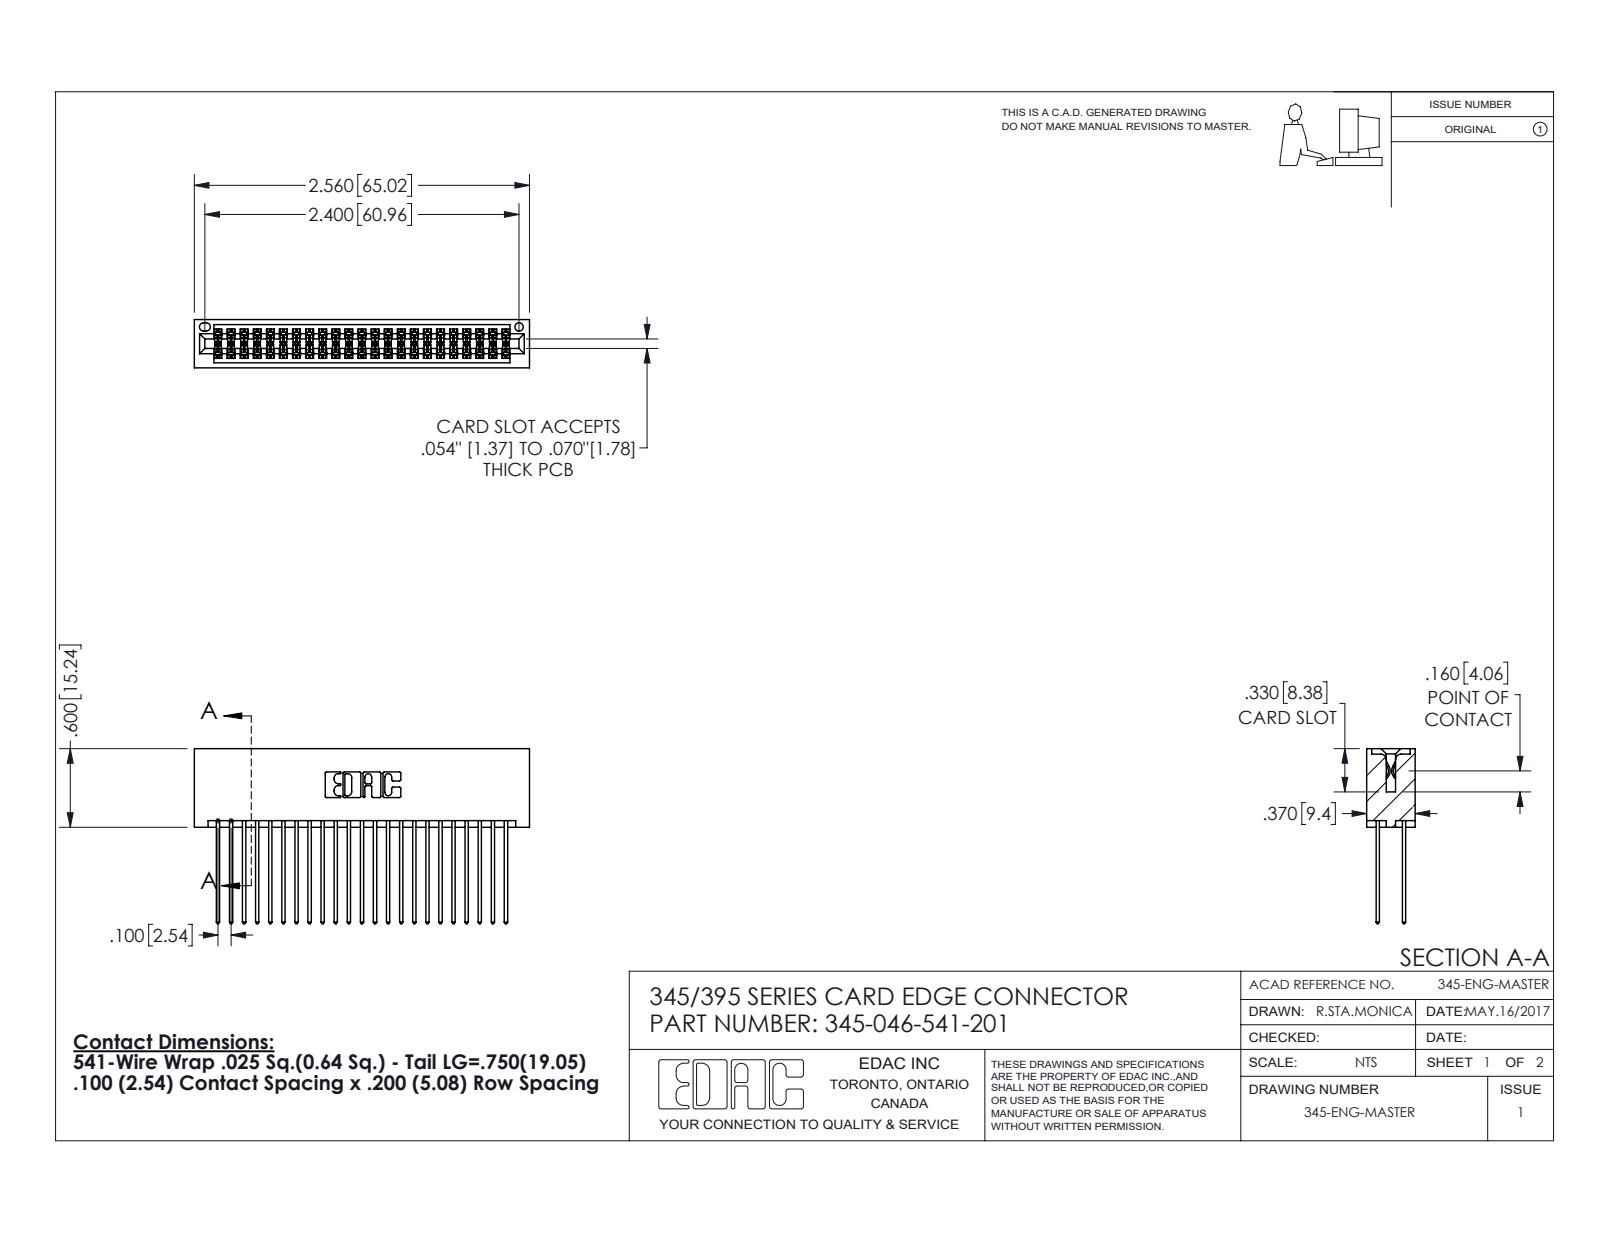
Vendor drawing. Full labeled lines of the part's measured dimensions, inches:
Part name (STEP PRODUCT): 345 Part_No Mounting Lugs; 345-292-001_345-293-141; 345-046-541-201
STEP written by: SolidWorks 2016 (CONFIG_CONTROL_DESIGN)
Units: inches
Bodies: 47 solids, 2418 faces (1594 planar, 824 cylindrical, 0 other)
Overall size (bounding box): 2.56 × 1.337 × 0.37
Volume: 0.428 in³ · Surface area: 17.91 in²
Round holes (diameter × count): ⌀0.064 ×1
Partial cylindrical surfaces — rounded edges, fillets, slot ends (radius × count): R0.006 ×69, R0.01 ×46, R0.01 ×22, R0.007 ×6, R0.031 ×6, R0.026 ×3, R0.014 ×2, R0.019 ×2
Main face-to-face distances: 0.298, 0.072, 0.2, 0.098, 0.272, 0.025, 0.225, 0.37, 0.175, 0.149
